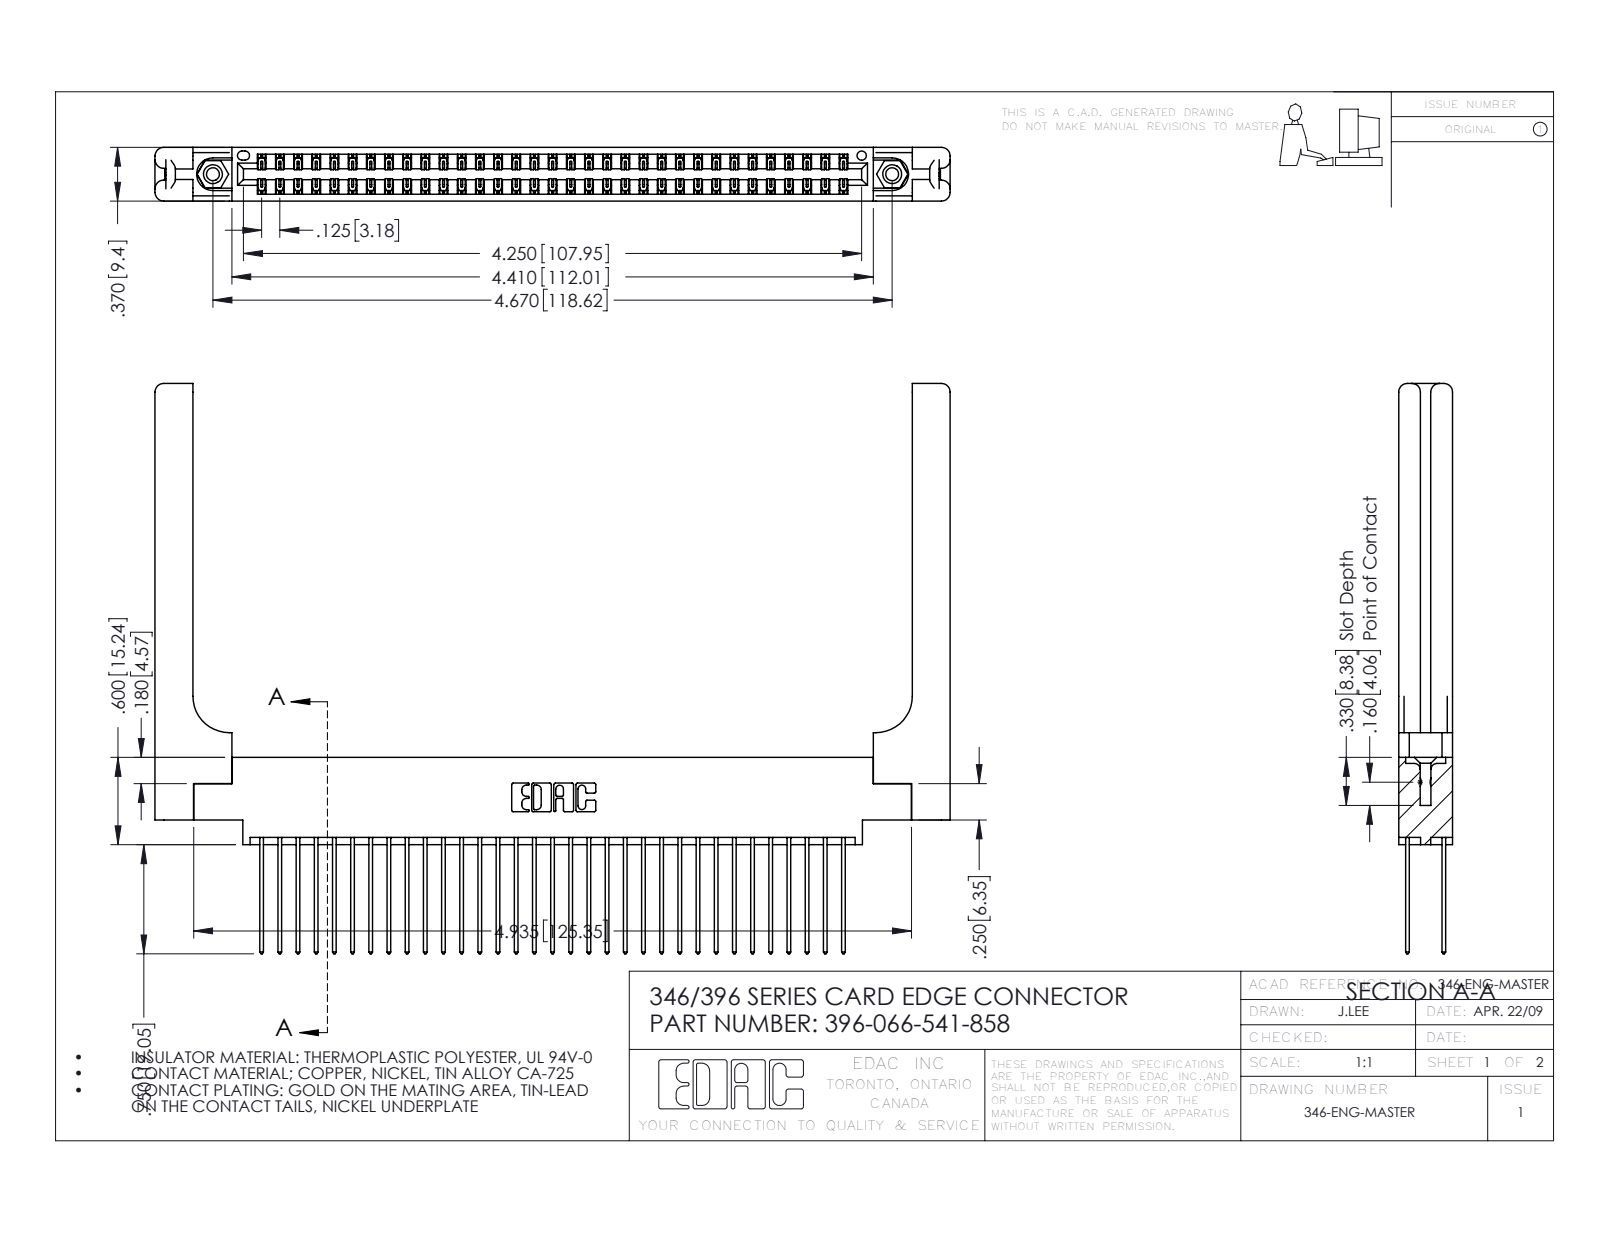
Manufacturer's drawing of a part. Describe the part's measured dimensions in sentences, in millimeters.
The part is named "346-220-058_345-220-058; 345-250-001_345-250-001-102; 346 Part_0.170 Offset - 0.156 Dia-TH; 396-066-541-858 (+1 more)". Its 3-D file was written by "SolidWorks 2016 (CONFIG_CONTROL_DESIGN)". It is 71 solids with 3814 faces: 2538 planar, 1216 cylindrical and 60 other. Overall it measures 138.8 by 99.6 by 9.4 millimeters. Its volume is 21 190 cubic millimeters and its surface area 25 650 square millimeters. Round holes: 2 of diameter 2.3, 2 of diameter 3.2, 2 of diameter 4, 1 of diameter 1.6. Round bosses or shafts: 2 of diameter 3.9. Partial cylindrical surfaces (rounded edges, fillets, slot ends): 99 of radius 0.2, 66 of radius 0.3, 22 of radius 0.3, 16 of radius 1.5, 6 of radius 0.2, 6 of radius 0.8, 3 of radius 0.7, 2 of radius 0.4. The main face-to-face distances are 1.2, 8.2, 1.8, 9.4, 6.4, 0.6, 7.6, 3.8, 3.8, 7. The hole center spacings are 6.2, 113.3, 118.6.
